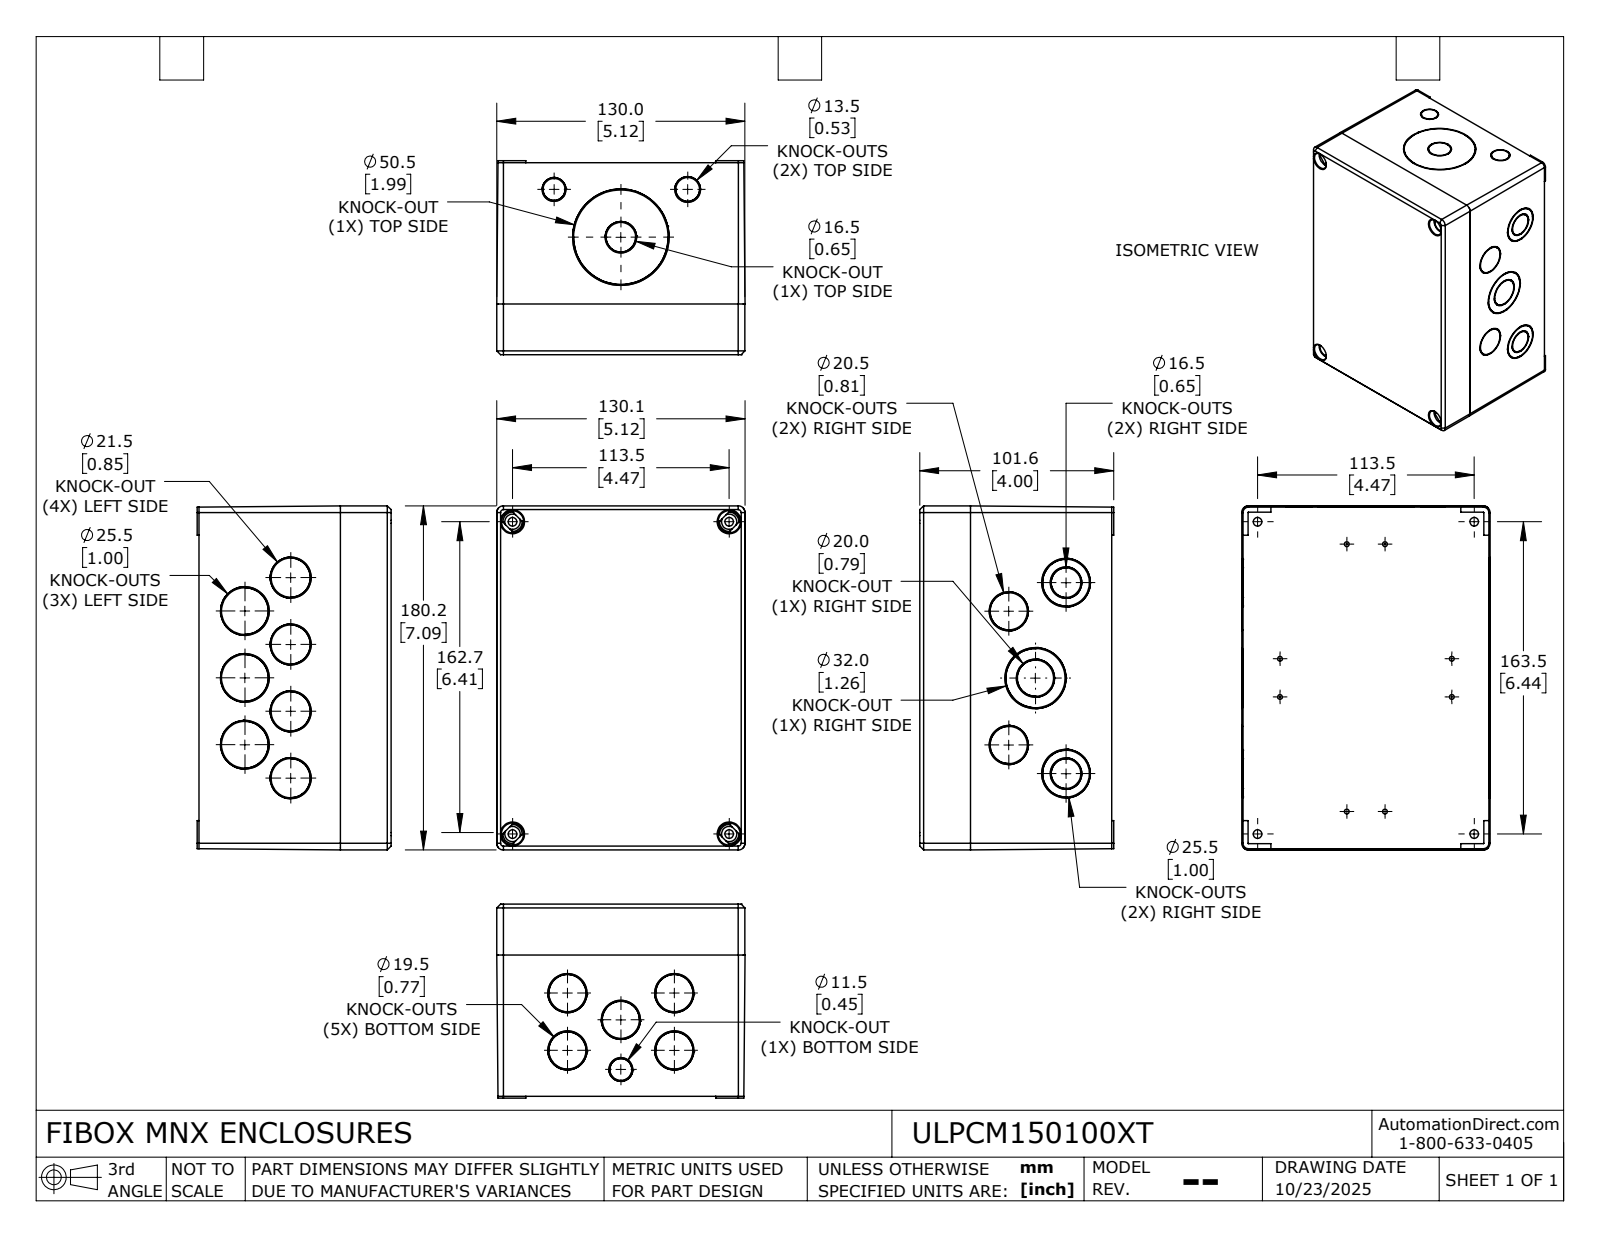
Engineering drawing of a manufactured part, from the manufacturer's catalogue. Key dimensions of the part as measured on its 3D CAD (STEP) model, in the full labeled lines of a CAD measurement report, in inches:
Part name (STEP PRODUCT): ULPCM150100XT
STEP written by: SolidWorks 2024 (AUTOMOTIVE_DESIGN)
Units: inches
Bodies: 2 solids, 906 faces (706 planar, 164 cylindrical, 36 other)
Overall size (bounding box): 7.094 × 5.122 × 4
Volume: 35.72 in³ · Surface area: 339.2 in²
Round holes (diameter × count): ⌀0.098 ×8, ⌀0.126 ×8, ⌀1.004 ×5, ⌀0.177 ×4, ⌀0.315 ×4, ⌀0.457 ×4, ⌀0.807 ×4, ⌀0.846 ×4, ⌀0.65 ×3, ⌀0.492 ×2, ⌀0.531 ×1, ⌀0.787 ×1
Round bosses / shafts (diameter × count): ⌀0.315 ×8, ⌀0.768 ×7, ⌀0.965 ×5, ⌀0.807 ×4, ⌀0.61 ×3, ⌀0.453 ×2, ⌀1.949 ×1, ⌀1.22 ×1
Partial cylindrical surfaces — rounded edges, fillets, slot ends (radius × count): R0.13 ×8, R0.404 ×6, R0.008 ×4, R0.102 ×4, R0.106 ×4, R0.112 ×4, R0.138 ×4, R0.198 ×4
Main face-to-face distances: 0.166, 3.961, 0.165, 3.795, 3.854, 3.689, 0.106, 1.047, 2.913, 2.748
Hole centre spacings: 0.394, 1.169, 1.378, 2.756, 3.543, 0.787, 1.333, 1.575
